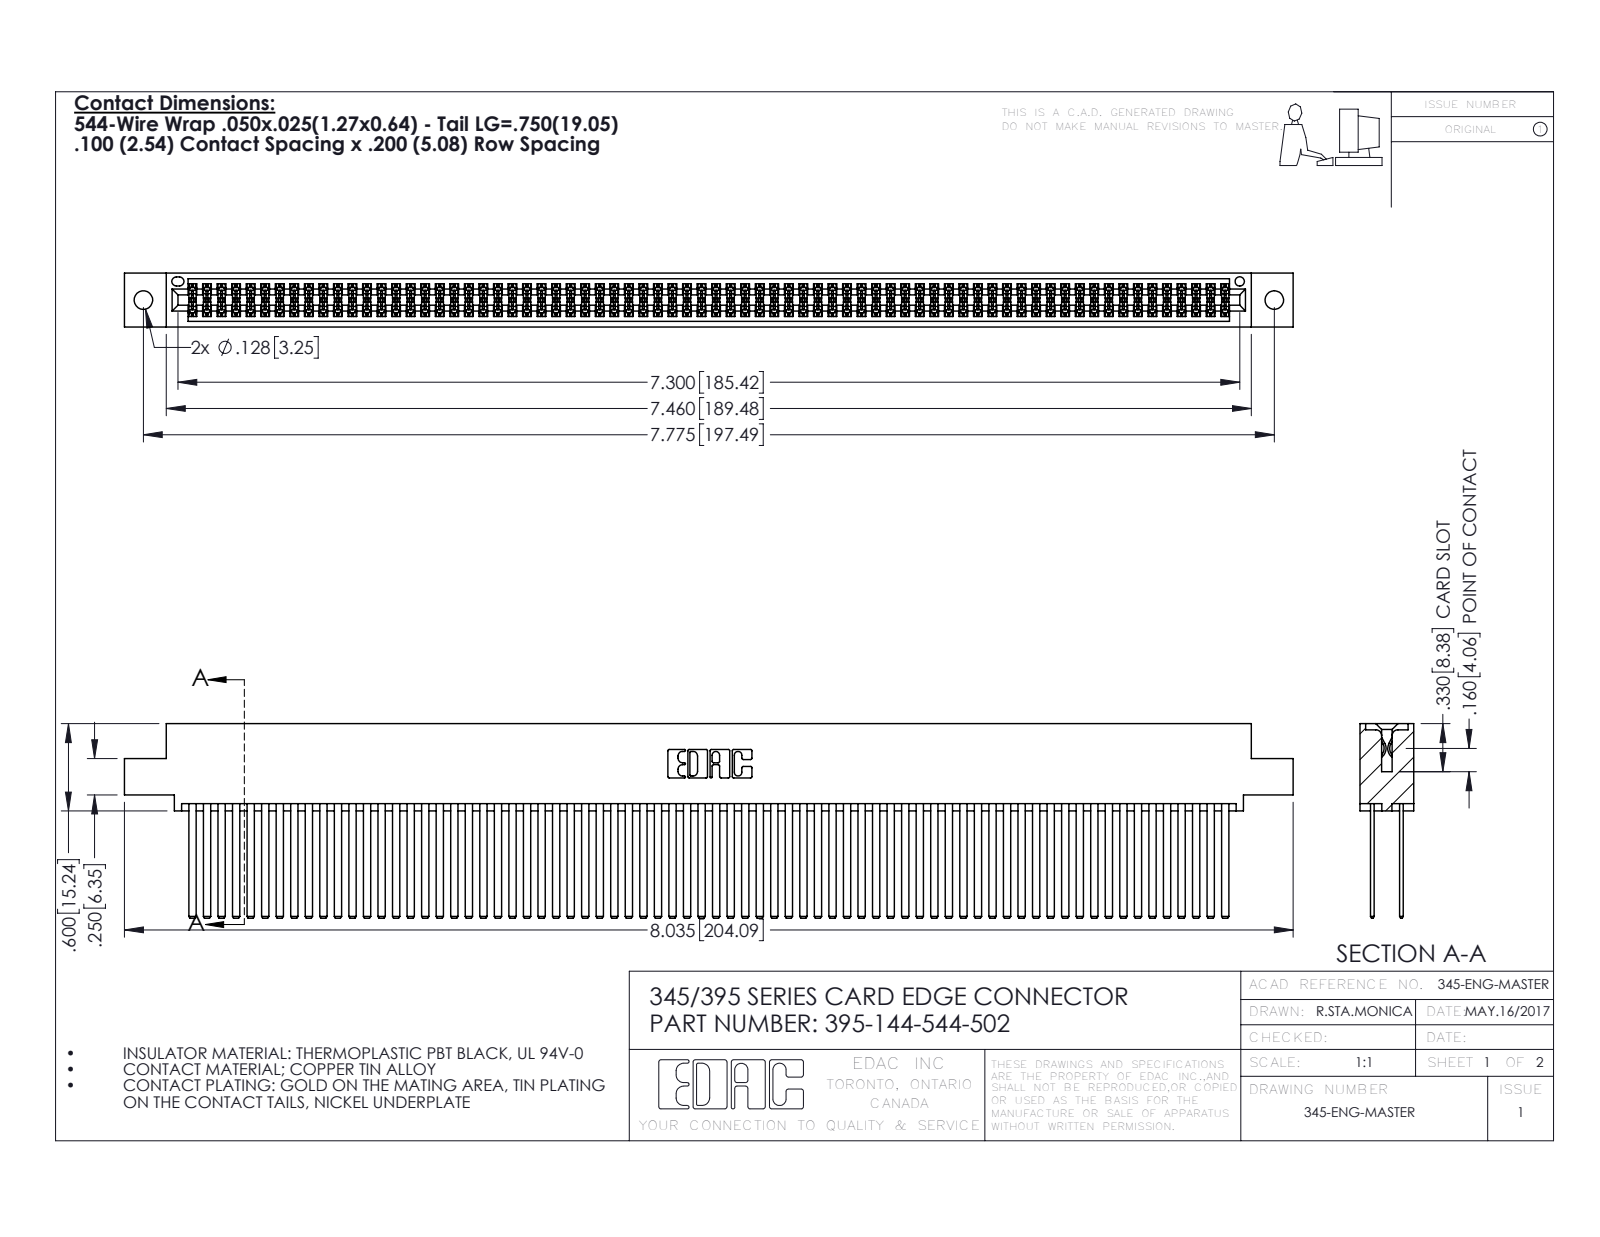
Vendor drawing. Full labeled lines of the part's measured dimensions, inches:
Part name (STEP PRODUCT): 395-144-544-502; 345 Part_0.110 Offset - 0.128 Dia; 345-292-001_345-293-144
STEP written by: SolidWorks 2016 (CONFIG_CONTROL_DESIGN)
Units: inches
Bodies: 145 solids, 6466 faces (4260 planar, 2206 cylindrical, 0 other)
Overall size (bounding box): 8.035 × 1.337 × 0.37
Volume: 1.343 in³ · Surface area: 60.23 in²
Round holes (diameter × count): ⌀0.128 ×2, ⌀0.064 ×1
Partial cylindrical surfaces — rounded edges, fillets, slot ends (radius × count): R0.006 ×216, R0.01 ×22, R0.007 ×6, R0.031 ×6, R0.026 ×3, R0.014 ×2, R0.019 ×2, R0.022 ×2
Main face-to-face distances: 0.2, 0.025, 0.298, 0.072, 0.098, 0.272, 0.225, 0.175, 0.37, 0.149
Hole centre spacings: 0.27, 7.539, 7.775
